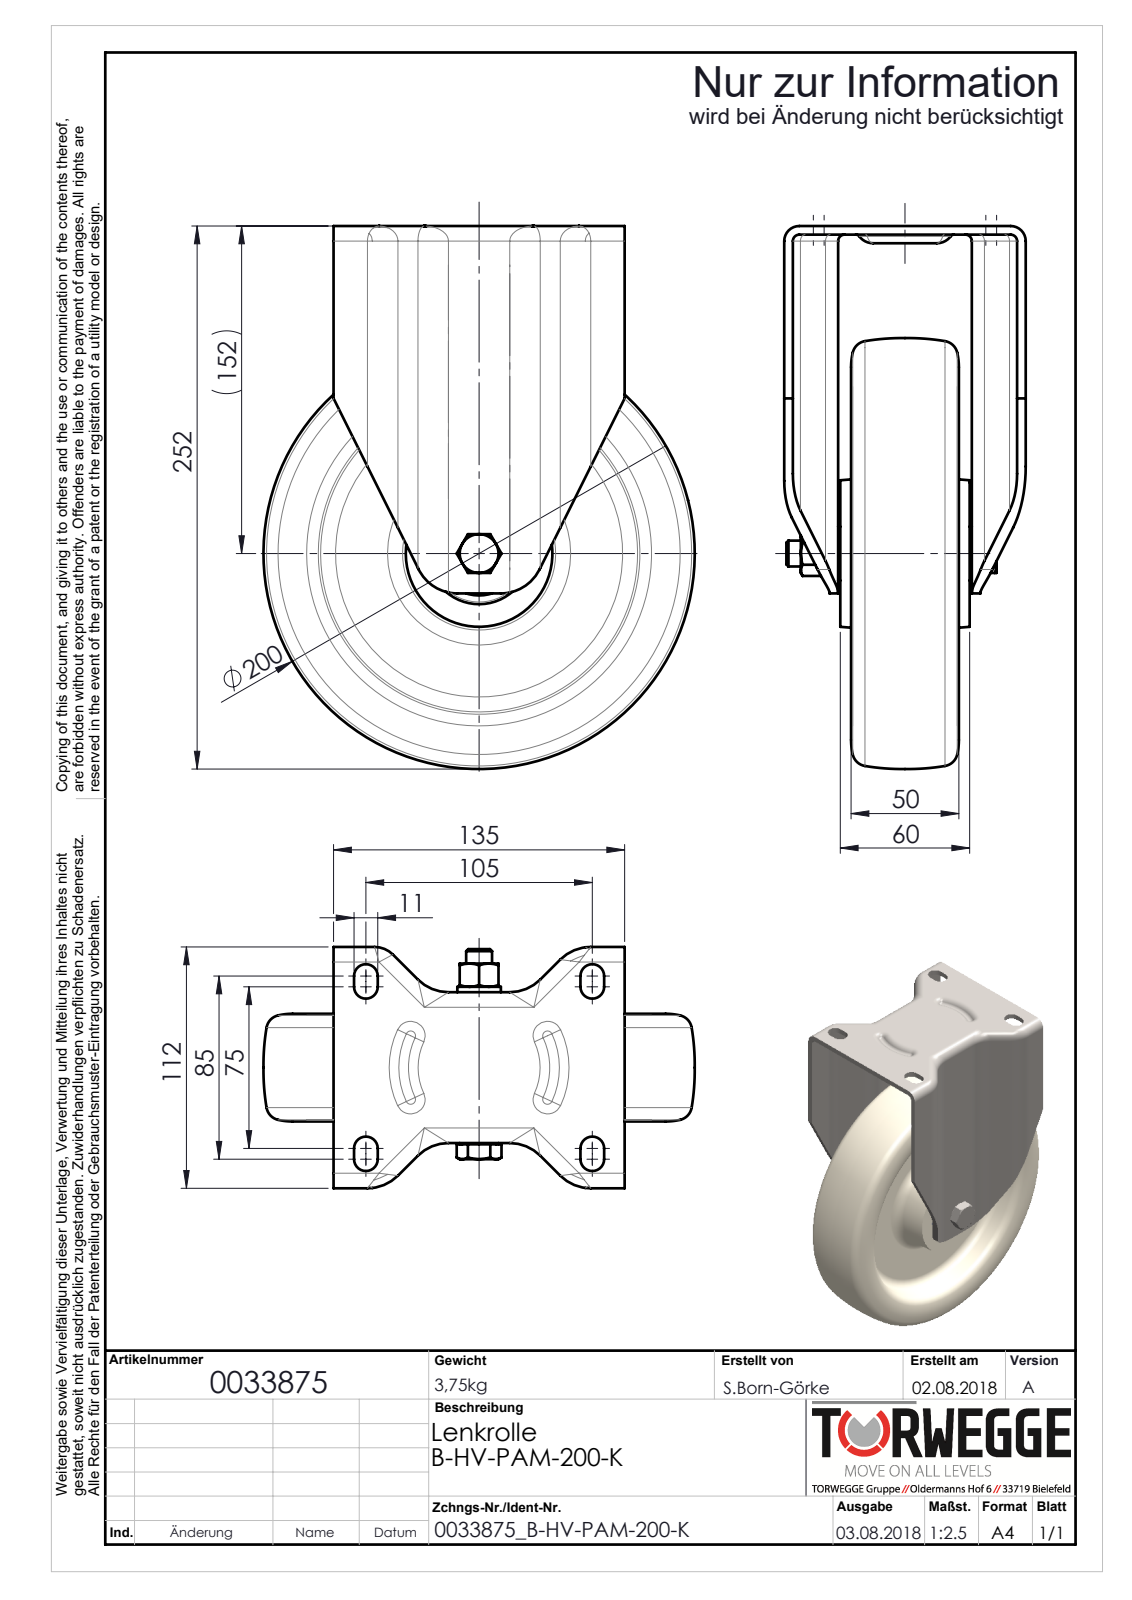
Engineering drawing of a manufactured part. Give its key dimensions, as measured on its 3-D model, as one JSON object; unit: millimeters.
{"part_name": "0033875_B-HV-PAM-200-K", "step_written_by": "SolidWorks 2018 (AUTOMOTIVE_DESIGN)", "units": "millimeters", "bodies": {"solids": 0, "faces": 319, "planar": 83, "cylindrical": 92, "other": 144}, "overall_size": [252.01, 200.02, 112], "round_holes": [[10.2, 1], [12, 1], [12.2, 1], [12.3, 1], [20, 1], [21, 1], [38.9, 1]], "round_bosses_or_shafts": [[28.1, 1], [25, 1], [20.2, 1], [19.9, 1], [18, 1]], "partial_cylinders_radius": [[20, 13], [3, 8], [5.5, 8], [7, 8], [12, 5]], "face_to_face_distances": [4, 21, 87, 25.5, 36.5, 29.5, 40.5, 66, 11, 13.68]}
